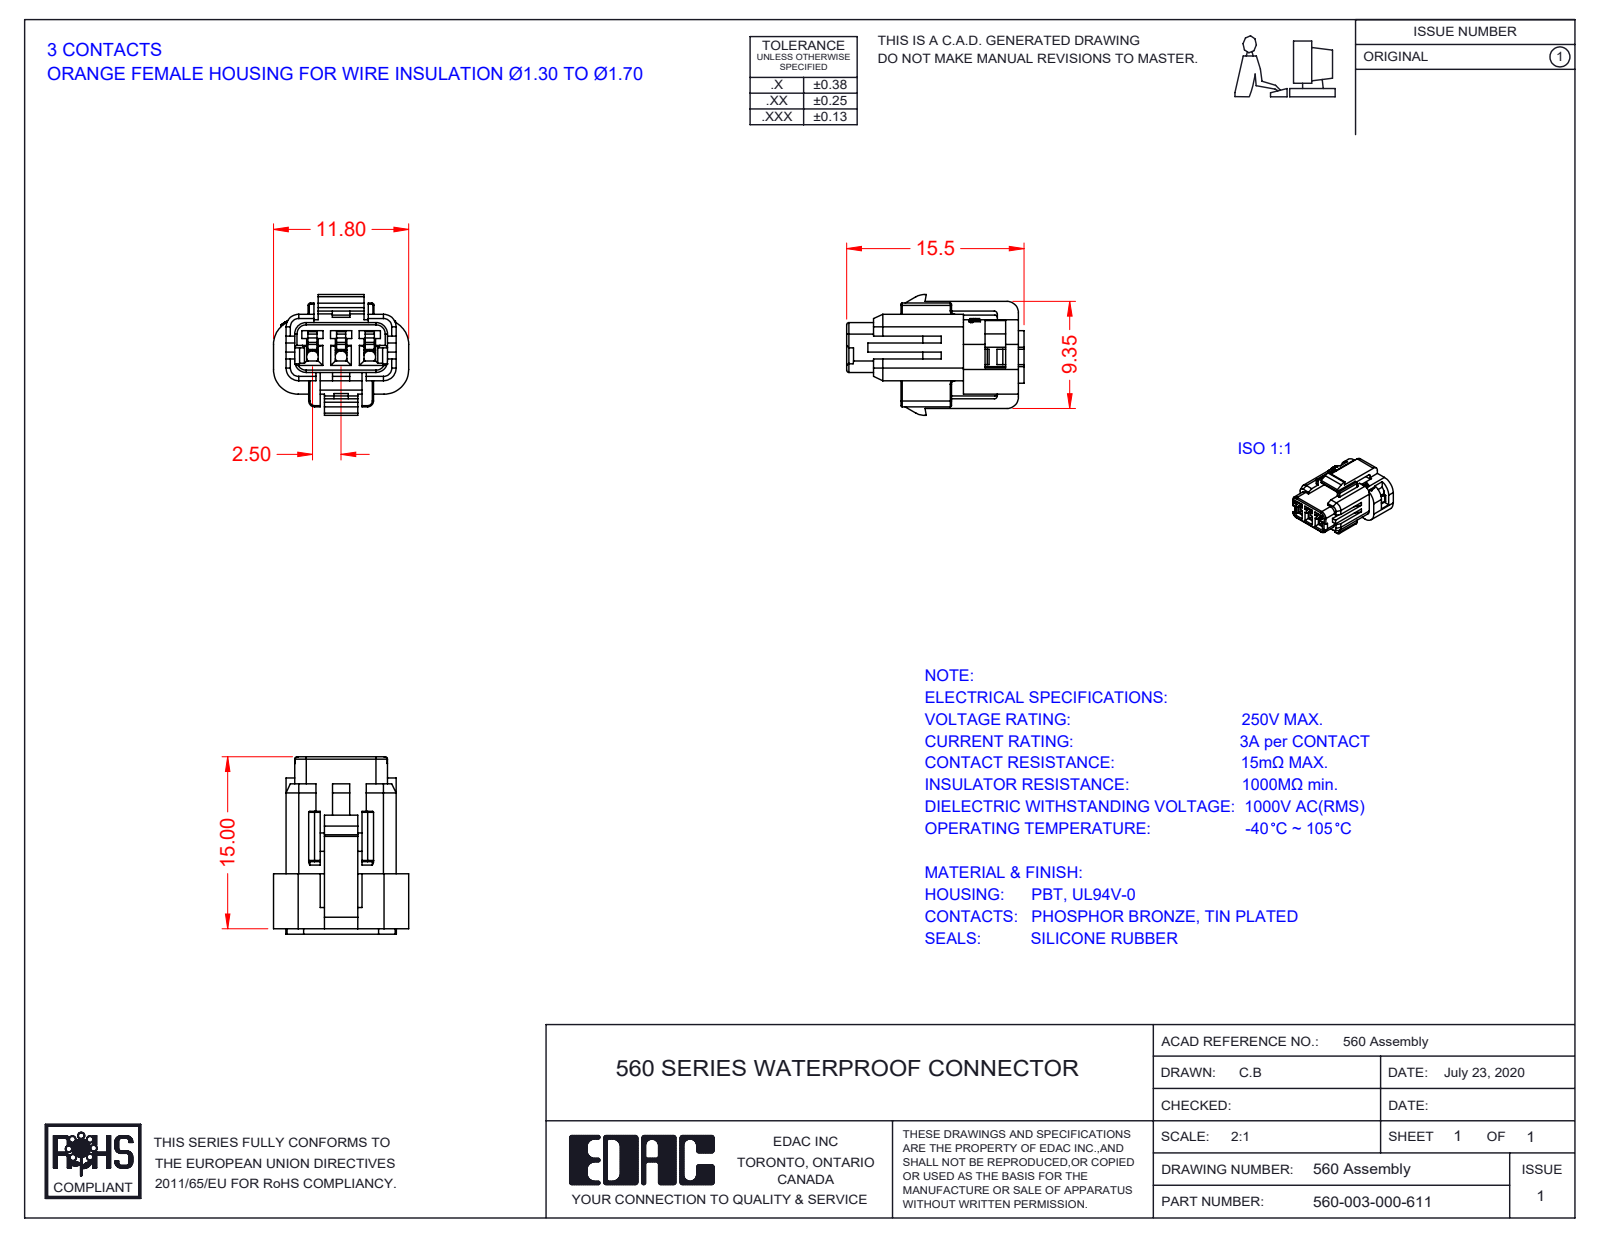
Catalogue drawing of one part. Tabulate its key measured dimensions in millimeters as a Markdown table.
| quantity | value |
| --- | --- |
| part name | REAR-GASKET-3POS_ORANGE; 560-003-000-611; REAR-INSULATOR-3POS-1; HOUSING-FEMALE-3POS_ORANGE |
| STEP written by | SolidWorks 2020 (CONFIG_CONTROL_DESIGN) |
| units | millimeters |
| bodies | 3 solids, 739 faces (457 planar, 142 cylindrical, 140 other) |
| overall size | 15.48 × 11.8 × 10.55 |
| volume | 722 mm³ |
| surface area | 1 761 mm² |
| round holes (diameter × count) | 1.5 × 3 |
| partial cylindrical surfaces (radius × count) | 0.1 × 13, 1.2 × 12, 0.2 × 10, 1 × 10, 0.15 × 8, 1.5 × 6, 0.3 × 4, 0.8 × 4 |
| main face-to-face distances | 0.7, 0.8, 3.8, 0.9, 2.5, 1.6, 1.85, 4, 3.1, 4.35 |
| hole center spacings | 2.5, 5 |
